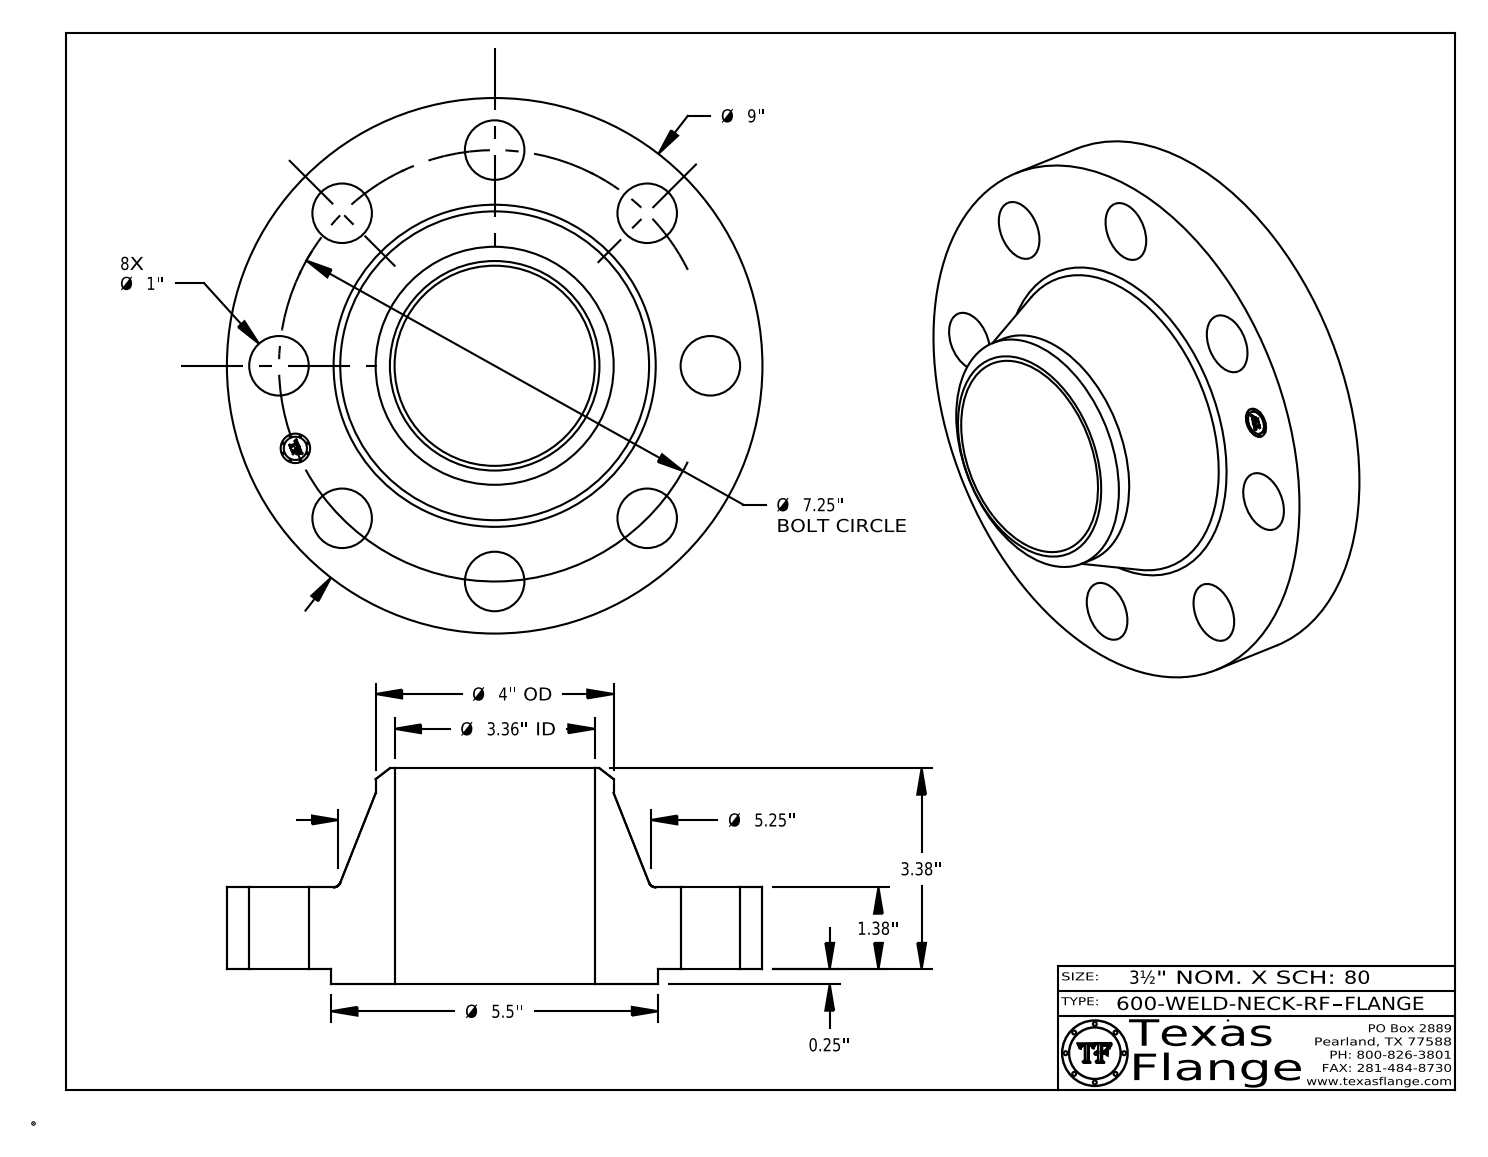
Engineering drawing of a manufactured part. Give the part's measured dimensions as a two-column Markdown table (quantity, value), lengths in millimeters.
| quantity | value |
| --- | --- |
| part name | 600-WELD-NECK-RF |
| STEP written by | CATIA V5 STEP AP214 (AUTOMOTIVE_DESIGN) |
| units | millimeters |
| bodies | 1 solid, 419 faces (369 planar, 44 cylindrical, 6 other) |
| overall size | 228.6 × 228.6 × 92.2 |
| volume | 1 385 000 mm³ |
| surface area | 149 900 mm² |
| round holes (diameter × count) | 25.4 × 8, 12.6 × 1, 85.4 × 1 |
| round bosses / shafts (diameter × count) | 0.8 × 8, 228.6 × 1, 139.7 × 1, 101.6 × 1, 9.9 × 1 |
| main face-to-face distances | 35.1, 6.4, 41.4, 92.2, 85.9, 50.8, 41, 34.7, 0.4, 51.2 |
| hole center spacings | 92.1, 70.5, 130.2, 170.1, 184.2, 35.9, 180.6, 102.3 |
